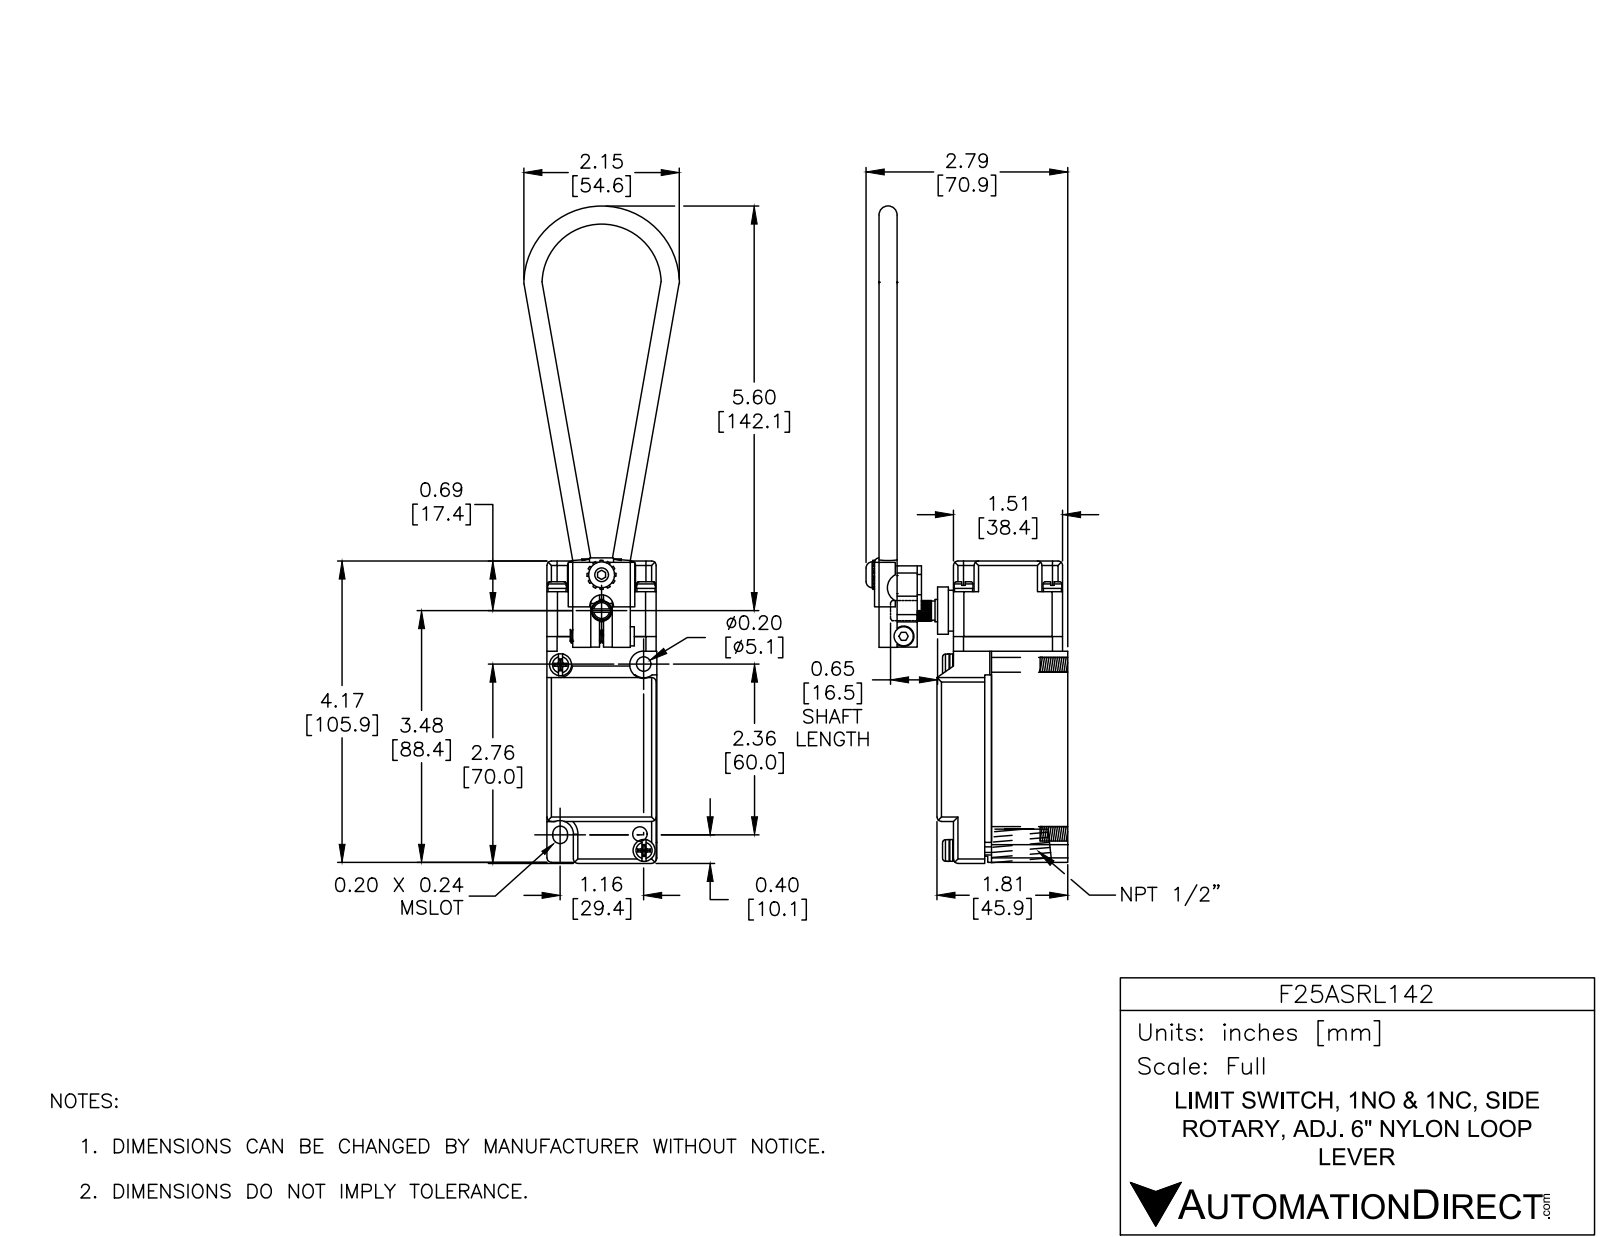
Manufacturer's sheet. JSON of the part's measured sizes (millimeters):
{"part_name": "F25ASRL142; Imported41; Imported40; Imported45 (+8 more)", "step_written_by": "SolidWorks 2002296 (CONFIG_CONTROL_DESIGN)", "units": "millimeters", "bodies": {"solids": 18, "faces": 1086, "planar": 523, "cylindrical": 250, "other": 313}, "overall_size": [241.1, 70.9, 54.6], "volume_mm3": 179900, "surface_area_mm2": 54150, "round_holes": [[4.5, 4], [5.1, 4], [4.8, 3], [2.8, 1], [5.1, 1], [5.2, 1], [5.3, 1], [7.2, 1], [14.7, 1]], "round_bosses_or_shafts": [[6.4, 8], [6.6, 4], [7.7, 2], [7.6, 2], [16.6, 1], [14.4, 1], [9.1, 1], [7.8, 1]], "partial_cylinders_radius": [[1.6, 32], [0.8, 16], [0.4, 8], [3.7, 8], [3.6, 4], [1, 2], [2.5, 2], [2.6, 2]], "face_to_face_distances": [2.4, 29.2, 26.8, 38.6, 16.8, 19.2, 45.9, 38.4, 5.8, 11], "hole_center_spacings": [31.2, 31.2, 44.2, 71.5, 5.7, 5.8, 6, 6.7]}
